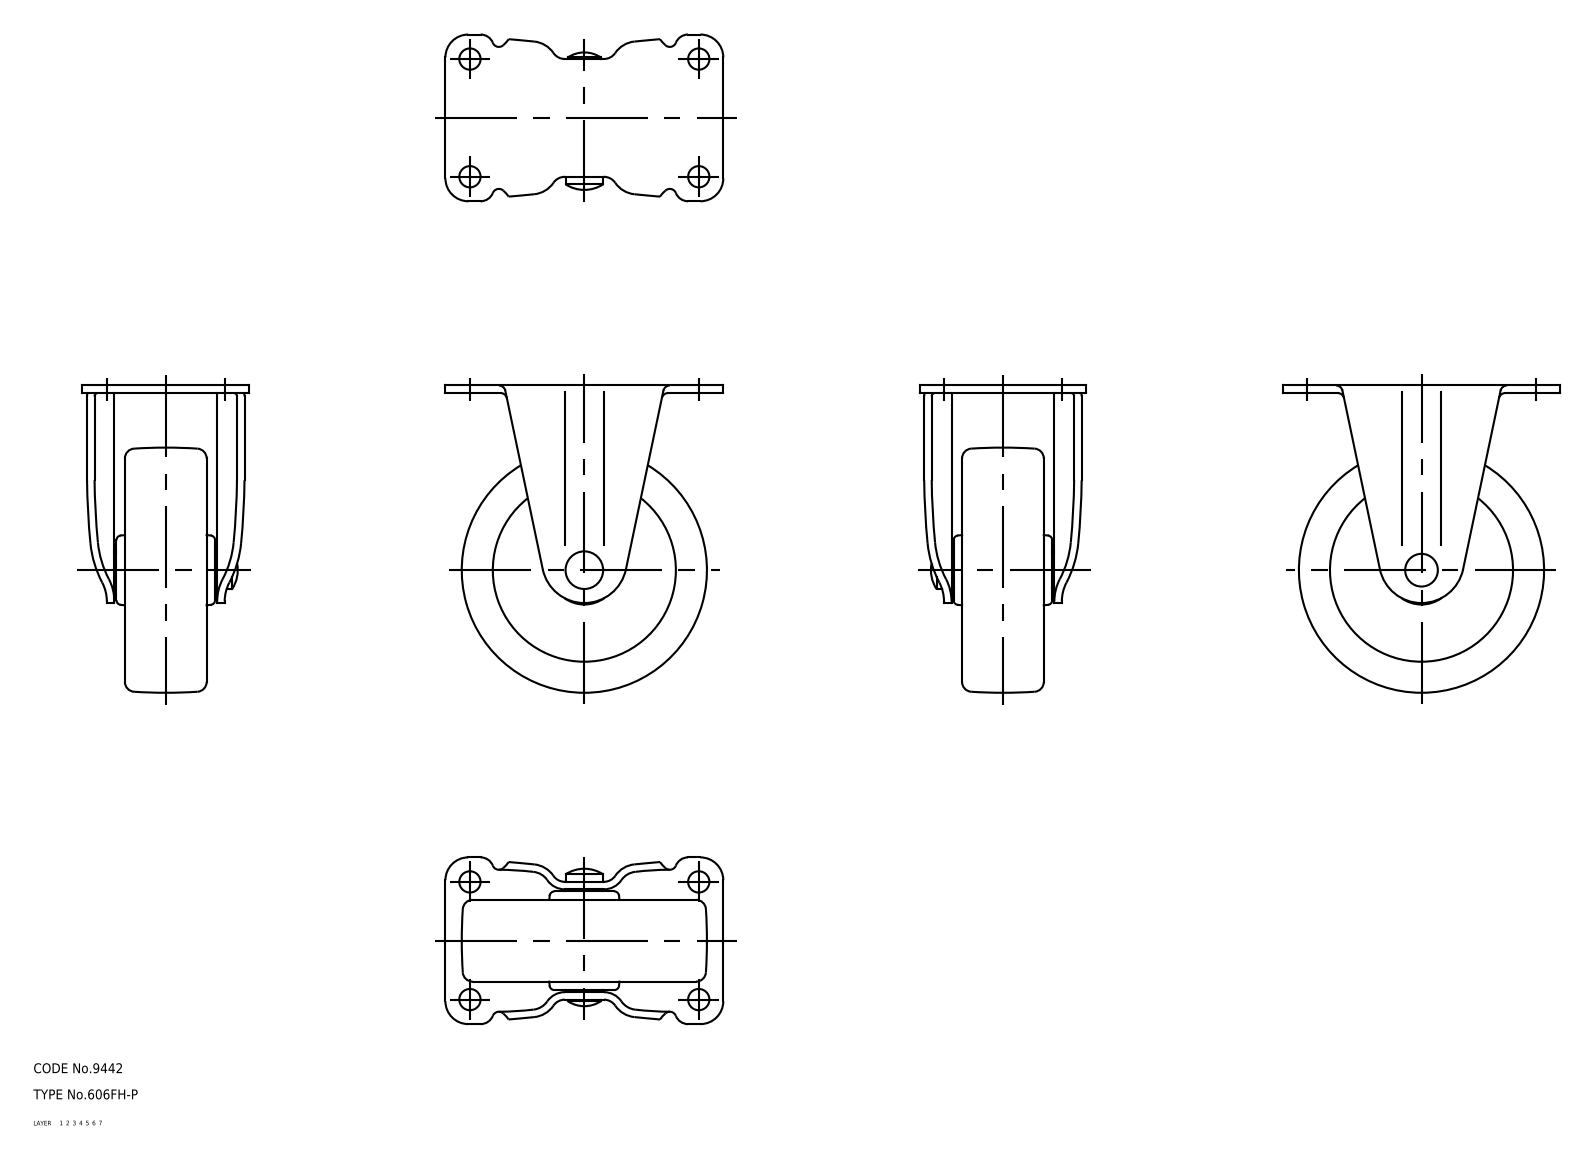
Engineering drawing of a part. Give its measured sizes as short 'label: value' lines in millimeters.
name: wheel; axle; No_606FH_P_16292_36
written by: CADfix (AUTOMOTIVE_DESIGN)
unit: mm
bodies: 3 solids, 172 faces (0 planar, 0 cylindrical, 172 other)
size: 94 × 85 × 51
volume: 109 428 mm³; area: 35 821 mm²
